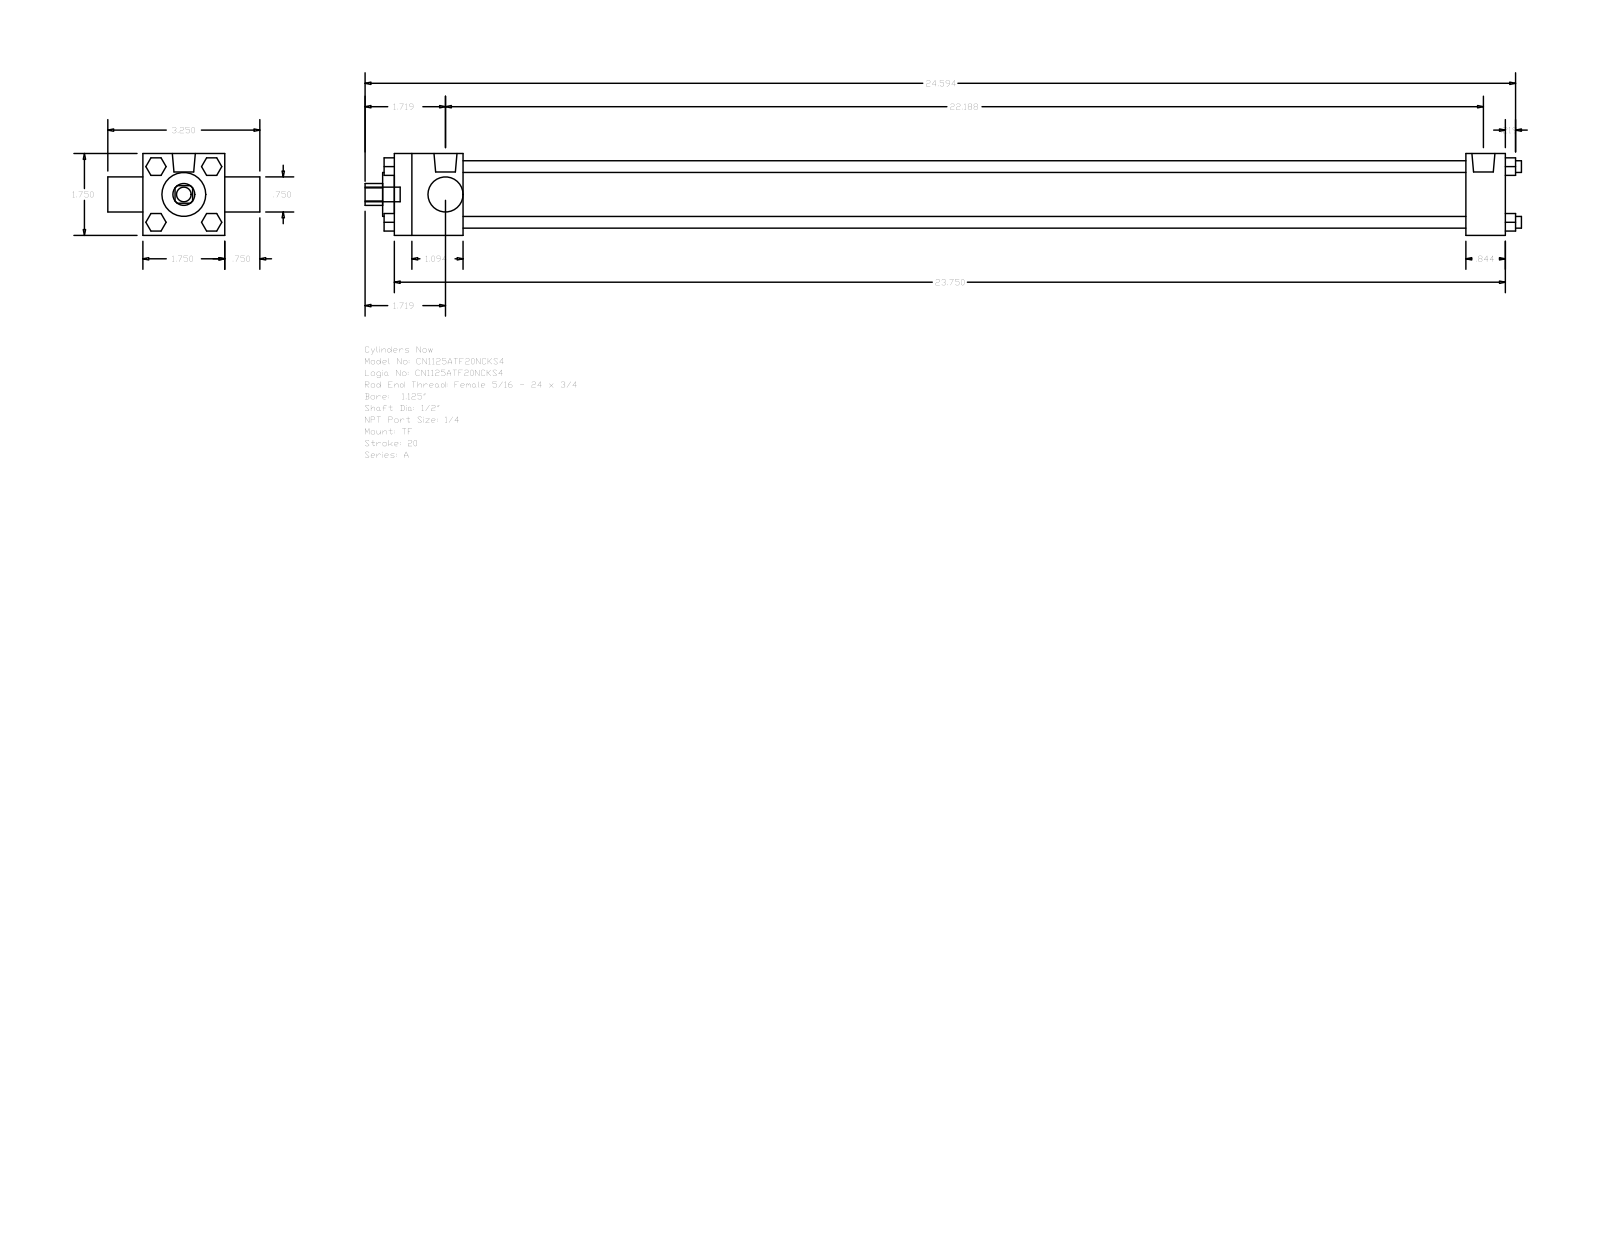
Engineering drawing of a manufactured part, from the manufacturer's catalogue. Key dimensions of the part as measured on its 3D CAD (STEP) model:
Part name (STEP PRODUCT): A_TF__0112_0.5
STEP written by: GSSL Pune (CONFIG_CONTROL_DESIGN)
Units: millimetres
Bodies: 0 solids, 120 faces (92 planar, 28 cylindrical, 0 other)
Overall size (bounding box): 627.86 × 82.55 × 44.45
Round holes (diameter × count): ⌀12.7 ×1, ⌀19.05 ×1, ⌀23.81 ×1, ⌀31.88 ×1
Round bosses / shafts (diameter × count): ⌀6.35 ×4, ⌀5.56 ×3, ⌀12.49 ×2, ⌀7.94 ×1
Partial cylindrical surfaces — rounded edges, fillets, slot ends (radius × count): R5.94 ×1
Main face-to-face distances: 44.46, 603.24, 581.81, 21.43, 37.3, 544.51, 565.94, 19.04, 63.5, 9.53
